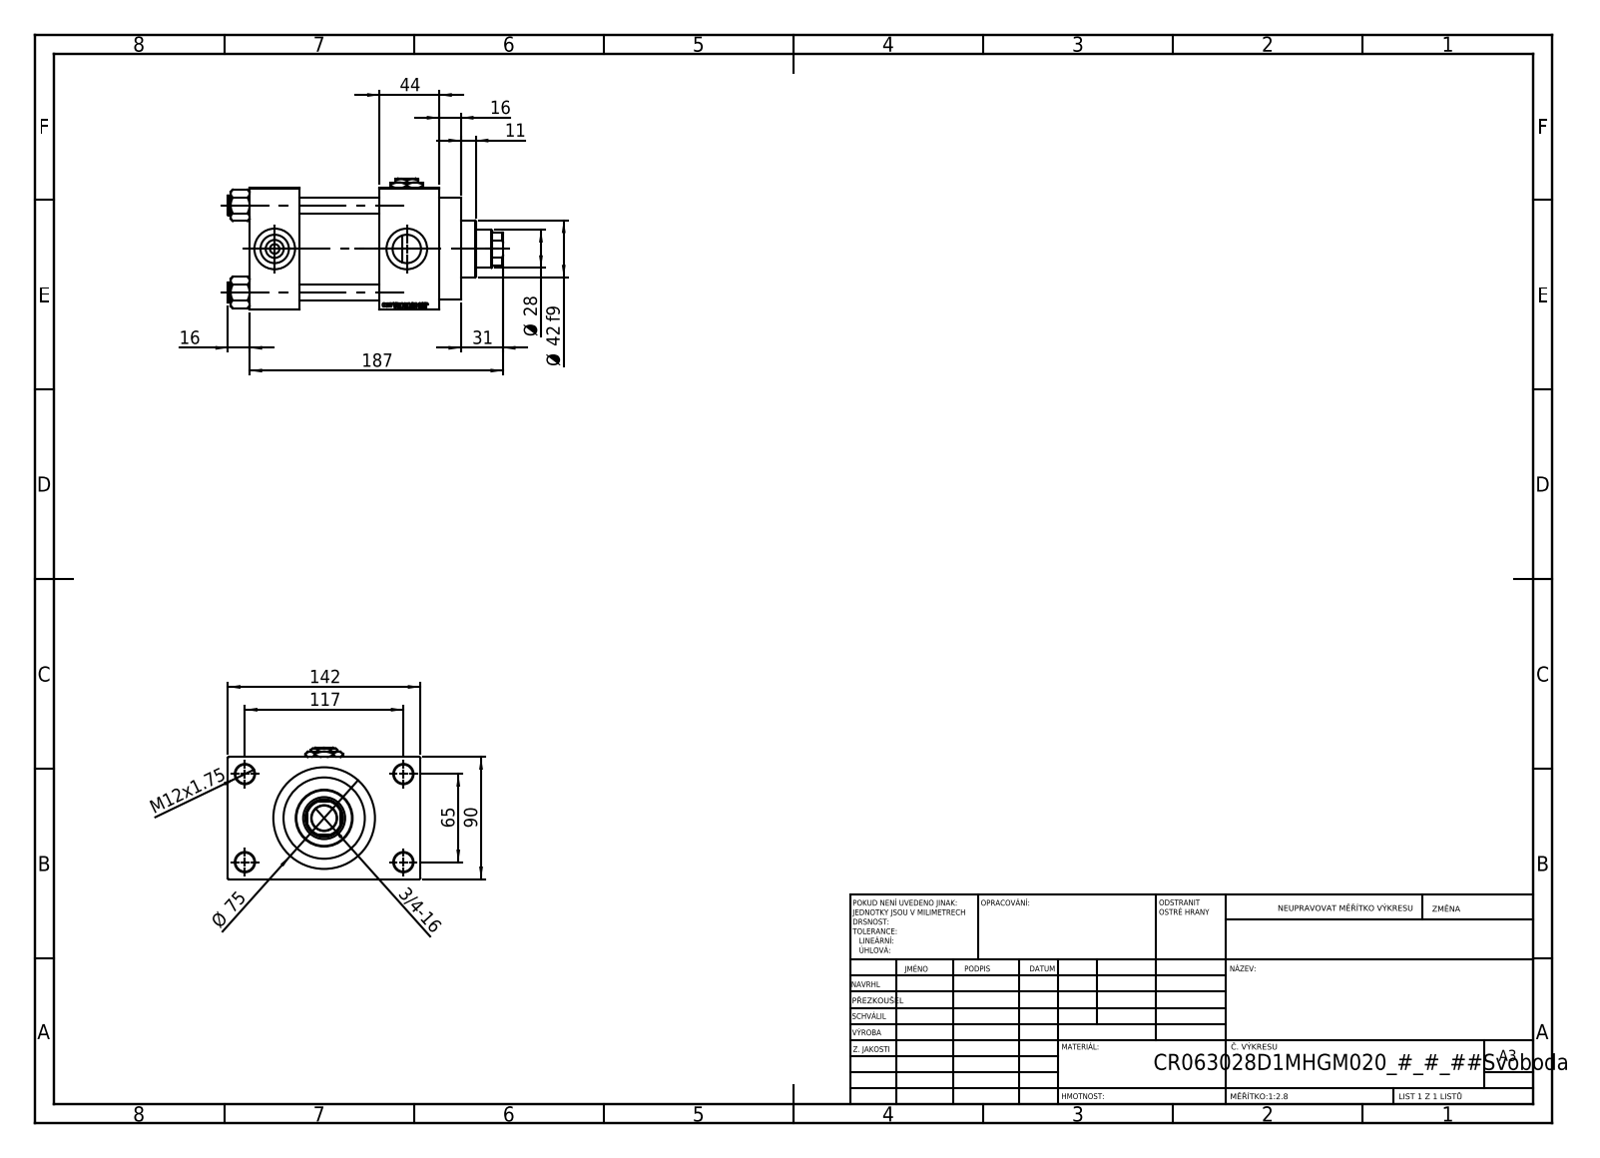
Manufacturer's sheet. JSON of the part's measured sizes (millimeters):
{"part_name": "Zatka_pro_OIL_PORT; V215CR_VCP_D; V215CR_D_TYCINKA; V215_VC_A (+2 more)", "step_written_by": "SolidWorks 2019 (CONFIG_CONTROL_DESIGN)", "units": "millimeters", "bodies": {"solids": 12, "faces": 1151, "planar": 521, "cylindrical": 92, "other": 538}, "overall_size": [203, 142, 97], "volume_mm3": 1093000, "surface_area_mm2": 202170, "round_holes": [[12, 4], [14, 4], [20.96, 3], [30, 3], [7, 2], [18.5, 1], [28, 1], [31, 1], [50, 1], [60, 1], [63, 1]], "round_bosses_or_shafts": [[15, 4], [75, 1], [69, 1], [42, 1]], "partial_cylinders_radius": [[13.5, 1]], "face_to_face_distances": [90, 59, 37, 96, 140, 103, 44, 26, 116, 16], "hole_center_spacings": [26.35, 45.47, 64.3, 66.92, 69.81, 90.65, 111.34, 65]}
